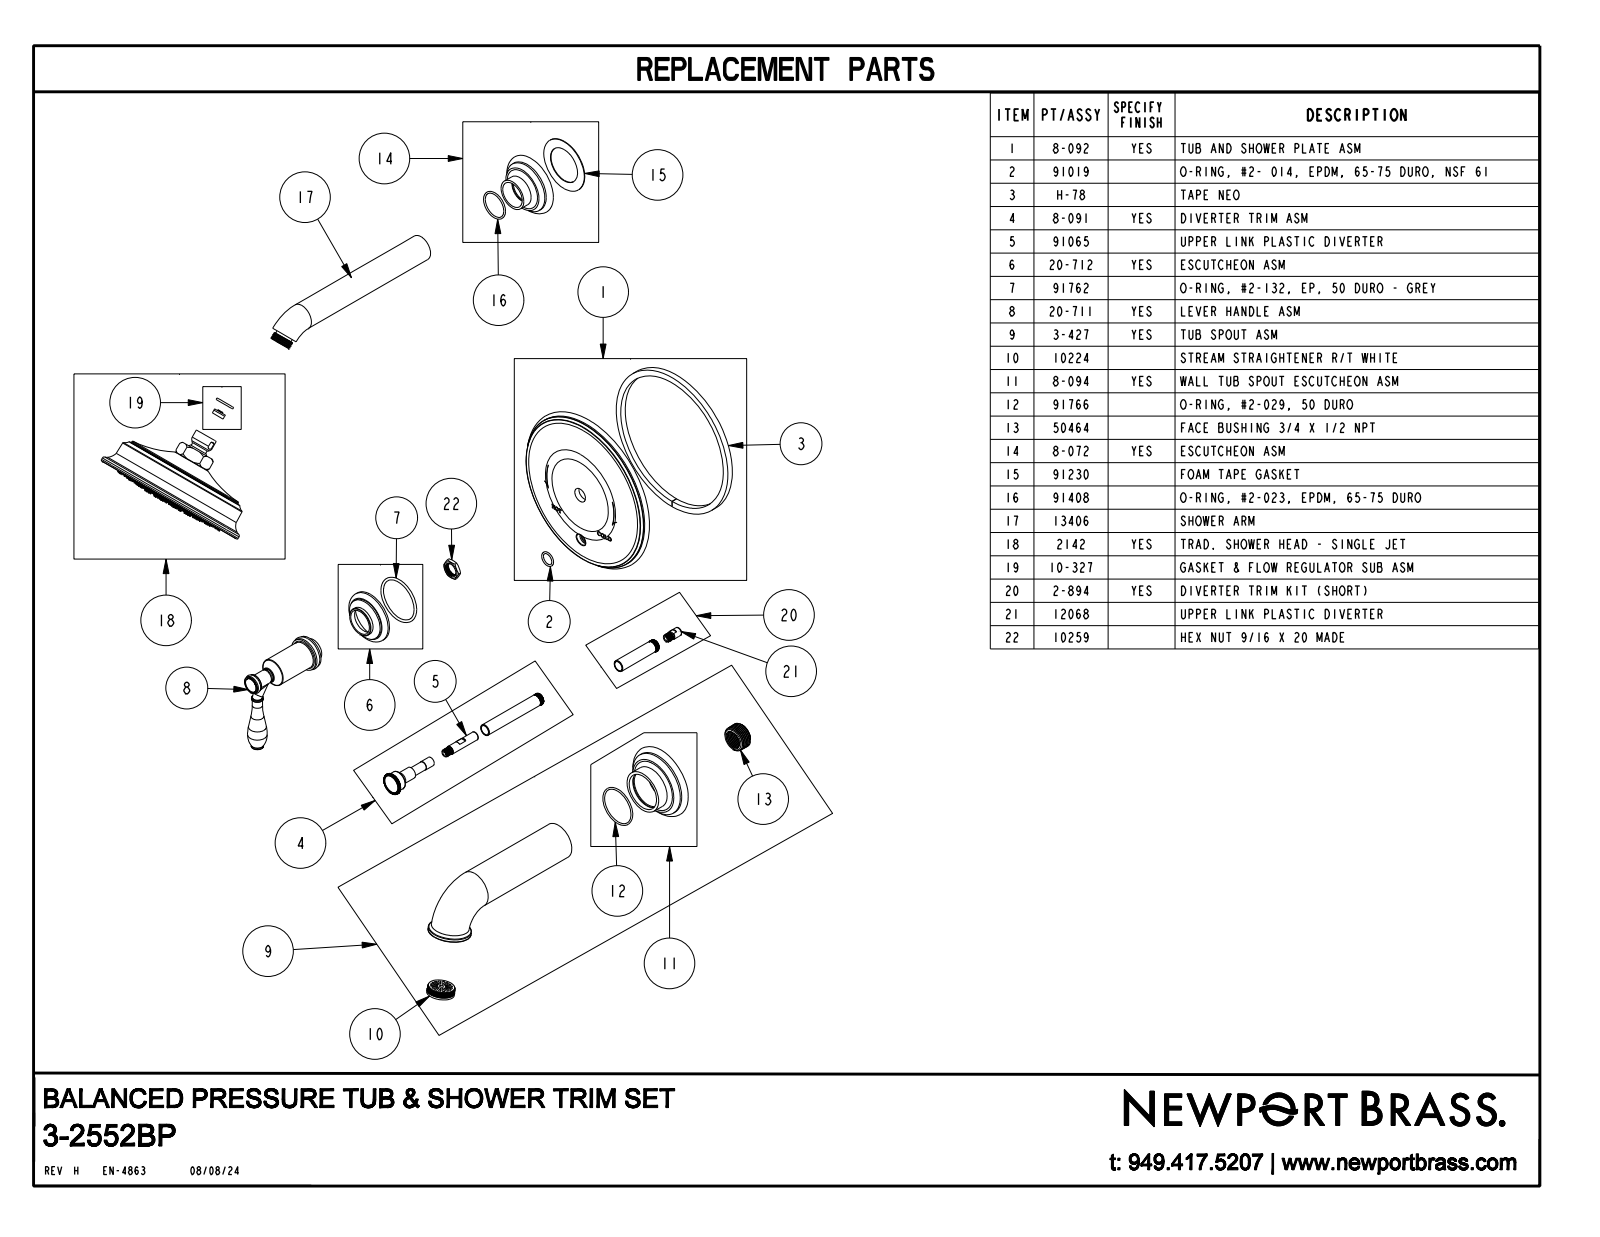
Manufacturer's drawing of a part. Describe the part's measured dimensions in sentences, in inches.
The part is named "3-2552BP". Its 3-D file was written by "CREO PARAMETRIC BY PTC INC, 2018400 (AUTOMOTIVE_DESIGN)". It is 42 solids with 2198 faces: 538 planar, 761 cylindrical and 899 other. Overall it measures 22.769 by 12.008 by 6.75 inches. Its volume is 71.06 cubic inches and its surface area 322.6 square inches. Round holes: 90 of diameter 0.05, 90 of diameter 0.125, 1 of diameter 0.22, 1 of diameter 0.394, 1 of diameter 0.5, 1 of diameter 0.59, 1 of diameter 0.6, 1 of diameter 0.604, 1 of diameter 1.2, 1 of diameter 5.275, 1 of diameter 5.7, 1 of diameter 6.25. Round bosses or shafts: 60 of diameter 0.198, 2 of diameter 6.2, 2 of diameter 2.11, 2 of diameter 1.1, 2 of diameter 0.6, 1 of diameter 6.51, 1 of diameter 5.5, 1 of diameter 4.83. Partial cylindrical surfaces (rounded edges, fillets, slot ends): 135 of radius 0.005, 1 of radius 0.25, 1 of radius 0.435. The main face-to-face distances are 0.25, 0.26, 0.48, 0.49, 0.23, 0.323, 0.313, 0.063, 0.167, 0.05. The hole center spacings are 0.48, 3.187, 1.408, 2.24, 0.952, 3.4, 3.555, 3.648.
